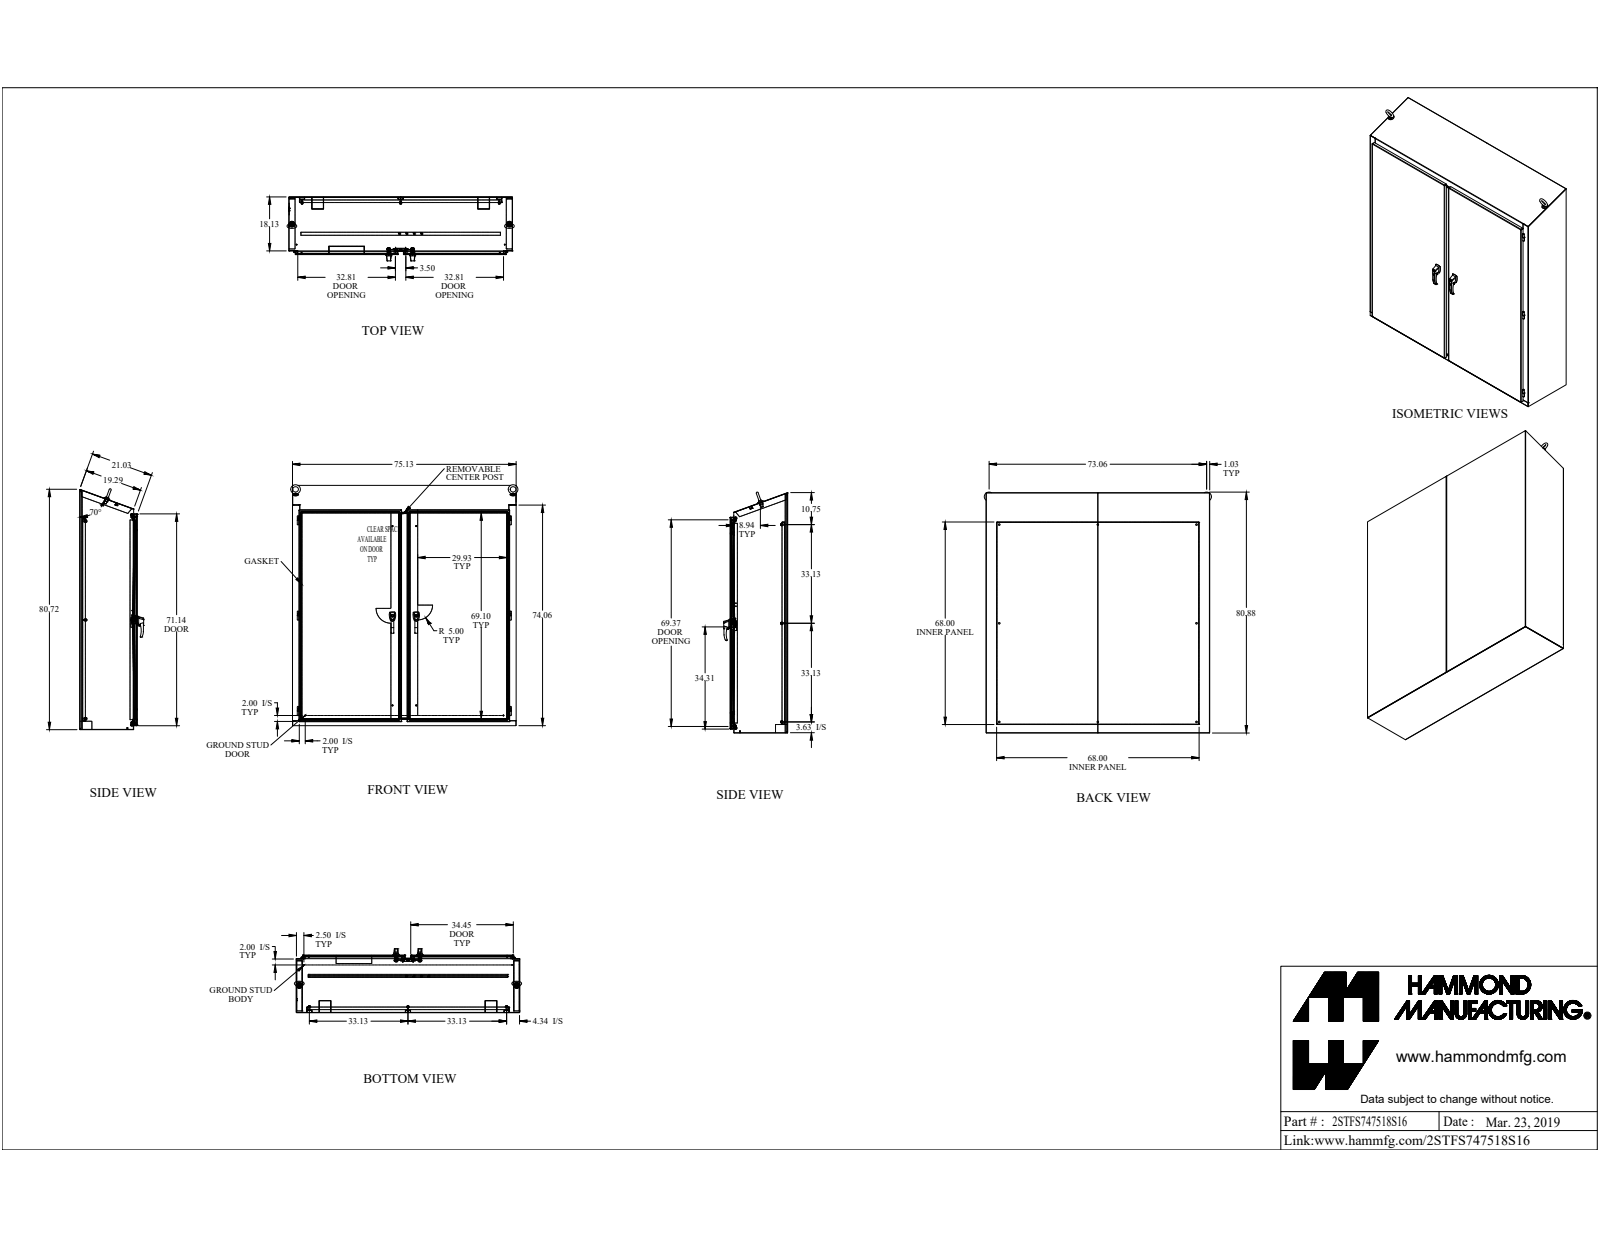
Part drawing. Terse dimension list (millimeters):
name: 2STFS747518S16
written by: SolidWorks 2019 (CONFIG_CONTROL_DESIGN)
unit: mm
bodies: 146 solids, 2404 faces (1417 planar, 729 cylindrical, 258 other)
size: 2054.5 × 1938.2 × 545.9
volume: 42 880 000 mm³; area: 33 610 000 mm²
holes: 8× ⌀7.8, 8× ⌀8.9, 8× ⌀14.3, 7× ⌀6.4, 6× ⌀7.1, 6× ⌀8, 6× ⌀11.3, 4× ⌀5, 4× ⌀6.5, 4× ⌀7.1, 4× ⌀9.9, 4× ⌀10.5
bosses: 12× ⌀25.4, 8× ⌀16.5, 8× ⌀9.5, 8× ⌀8.4, 4× ⌀19.1, 4× ⌀16, 4× ⌀15.9, 4× ⌀11.2
rounds: 47× R3.2, 33× R12.7, 32× R0.5, 30× R1.2, 30× R3.6, 20× R1.5, 16× R6.4, 12× R0.8
face distances: 2.4, 2.4, 487.3, 489.7, 489.7, 492.2, 3.2, 443.7, 441.3, 46
hole spacings: 1855.7, 202.8, 1881.4, 1682.8, 28.6, 32.7, 189.1, 204.8
